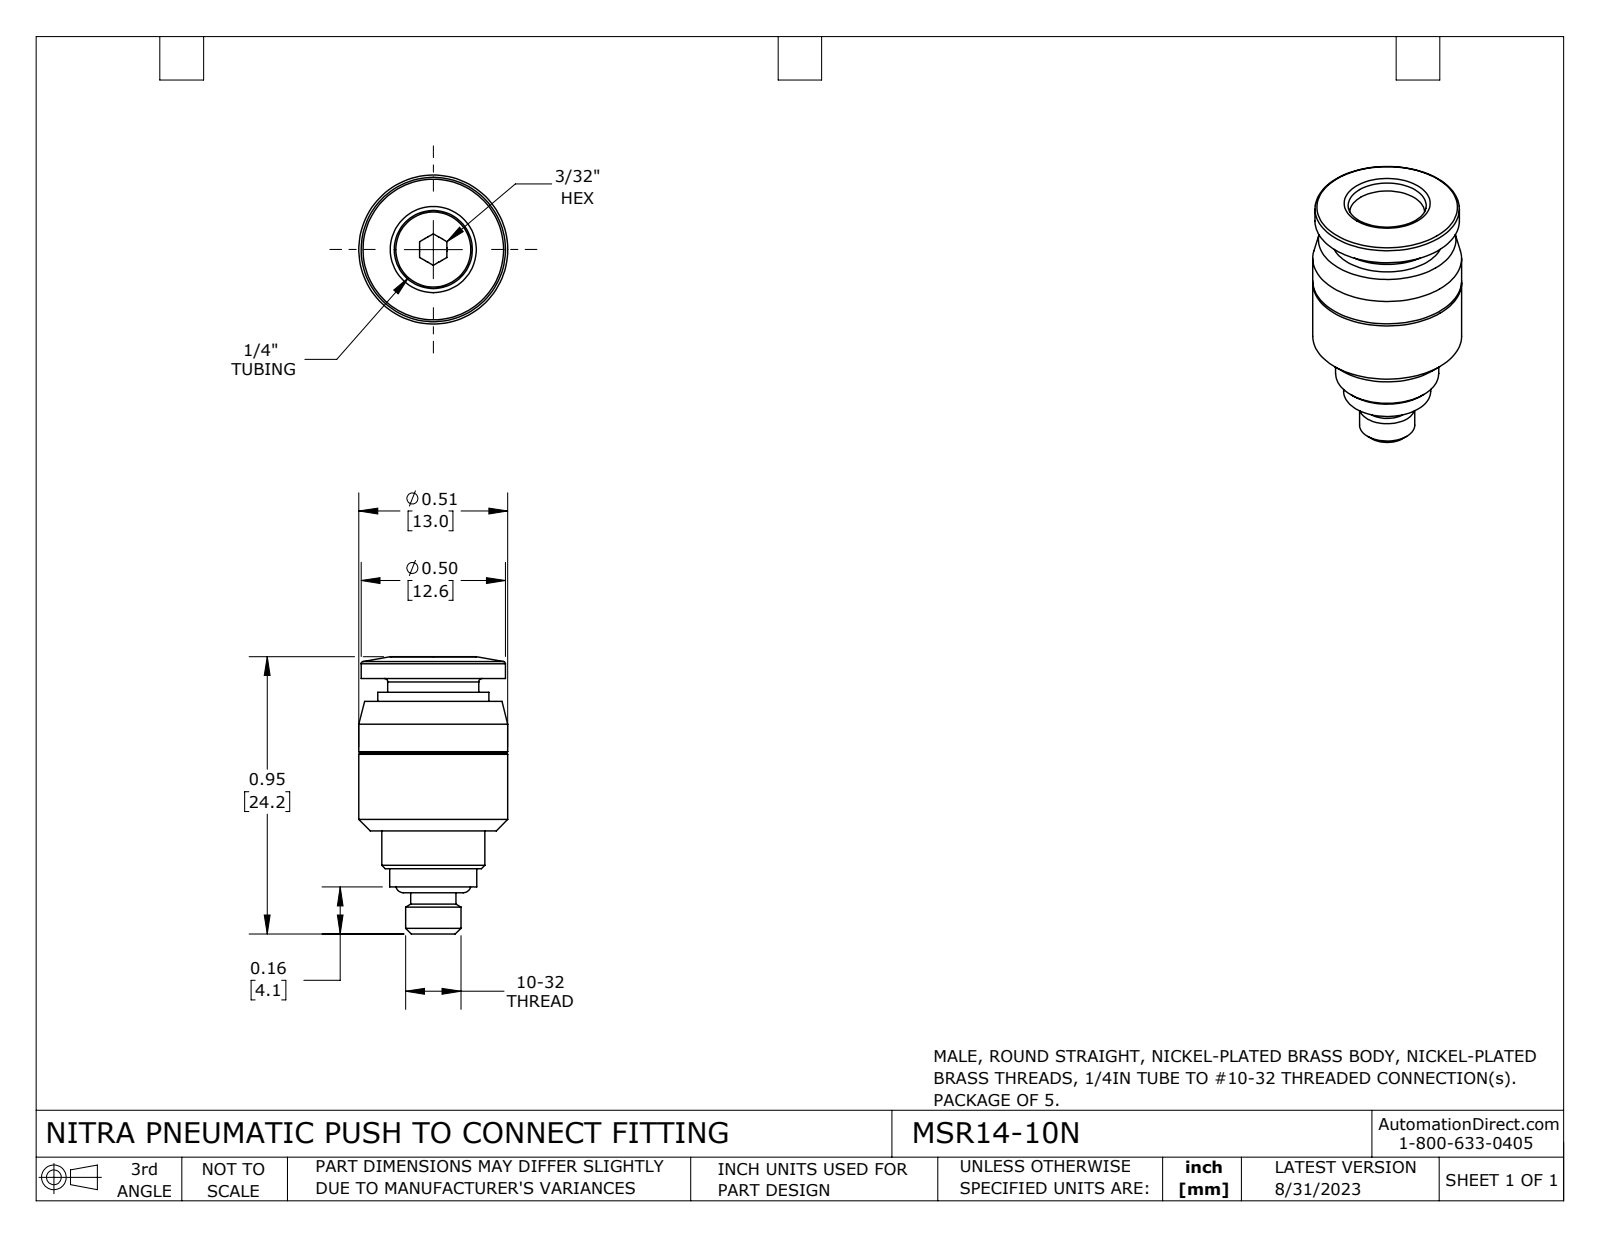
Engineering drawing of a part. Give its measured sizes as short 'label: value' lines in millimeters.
name: MSR14-10N
written by: SolidWorks 2015 (AUTOMOTIVE_DESIGN)
unit: mm
bodies: 2 solids, 66 faces (10 planar, 24 cylindrical, 32 other)
size: 24.2 × 13 × 13
volume: 1 500 mm³; area: 1 613 mm²
holes: 1× ⌀2.4, 1× ⌀6.6
bosses: 1× ⌀13, 1× ⌀12.6, 1× ⌀9.7, 1× ⌀9, 1× ⌀8, 1× ⌀7.6, 1× ⌀4.8, 1× ⌀4
face distances: 0.8, 2, 11.3, 13.3, 1.7, 13, 15, 15.4, 13.8, 12.1
